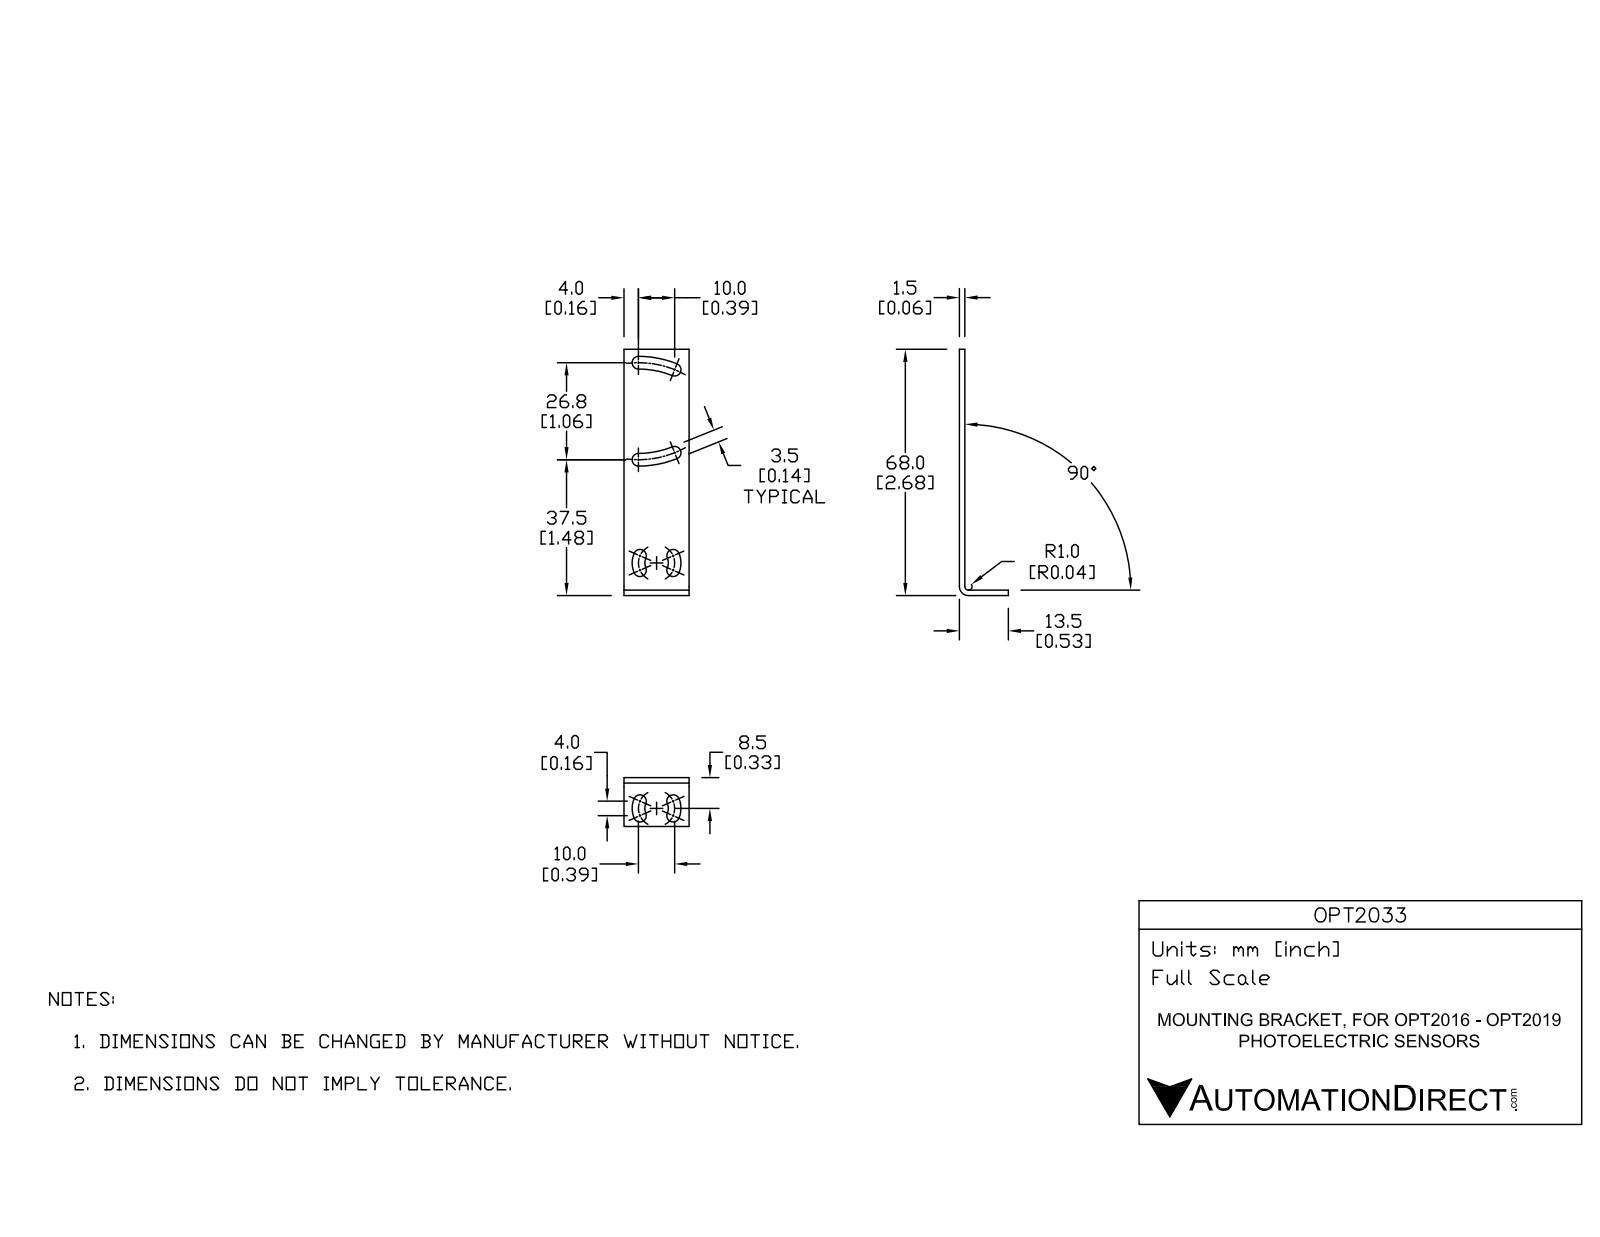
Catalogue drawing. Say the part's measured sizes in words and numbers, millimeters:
Its 3-D file was written by "Unknown (CONFIG_CONTROL_DESIGN)". It is 1 solid with 34 faces: 8 planar, 26 cylindrical and 0 other. Overall it measures 68 by 18 by 13.5 millimeters. Its volume is 1 859 cubic millimeters and its surface area 2 980 square millimeters. Partial cylindrical surfaces (rounded edges, fillets, slot ends): 12 of radius 1.75, 2 of radius 3.25, 2 of radius 6.75, 2 of radius 25.05, 2 of radius 28.55, 1 of radius 1, 1 of radius 2.5. The main face-to-face distances are 1.5, 18, 12, 13.5, 68, 66.5.
